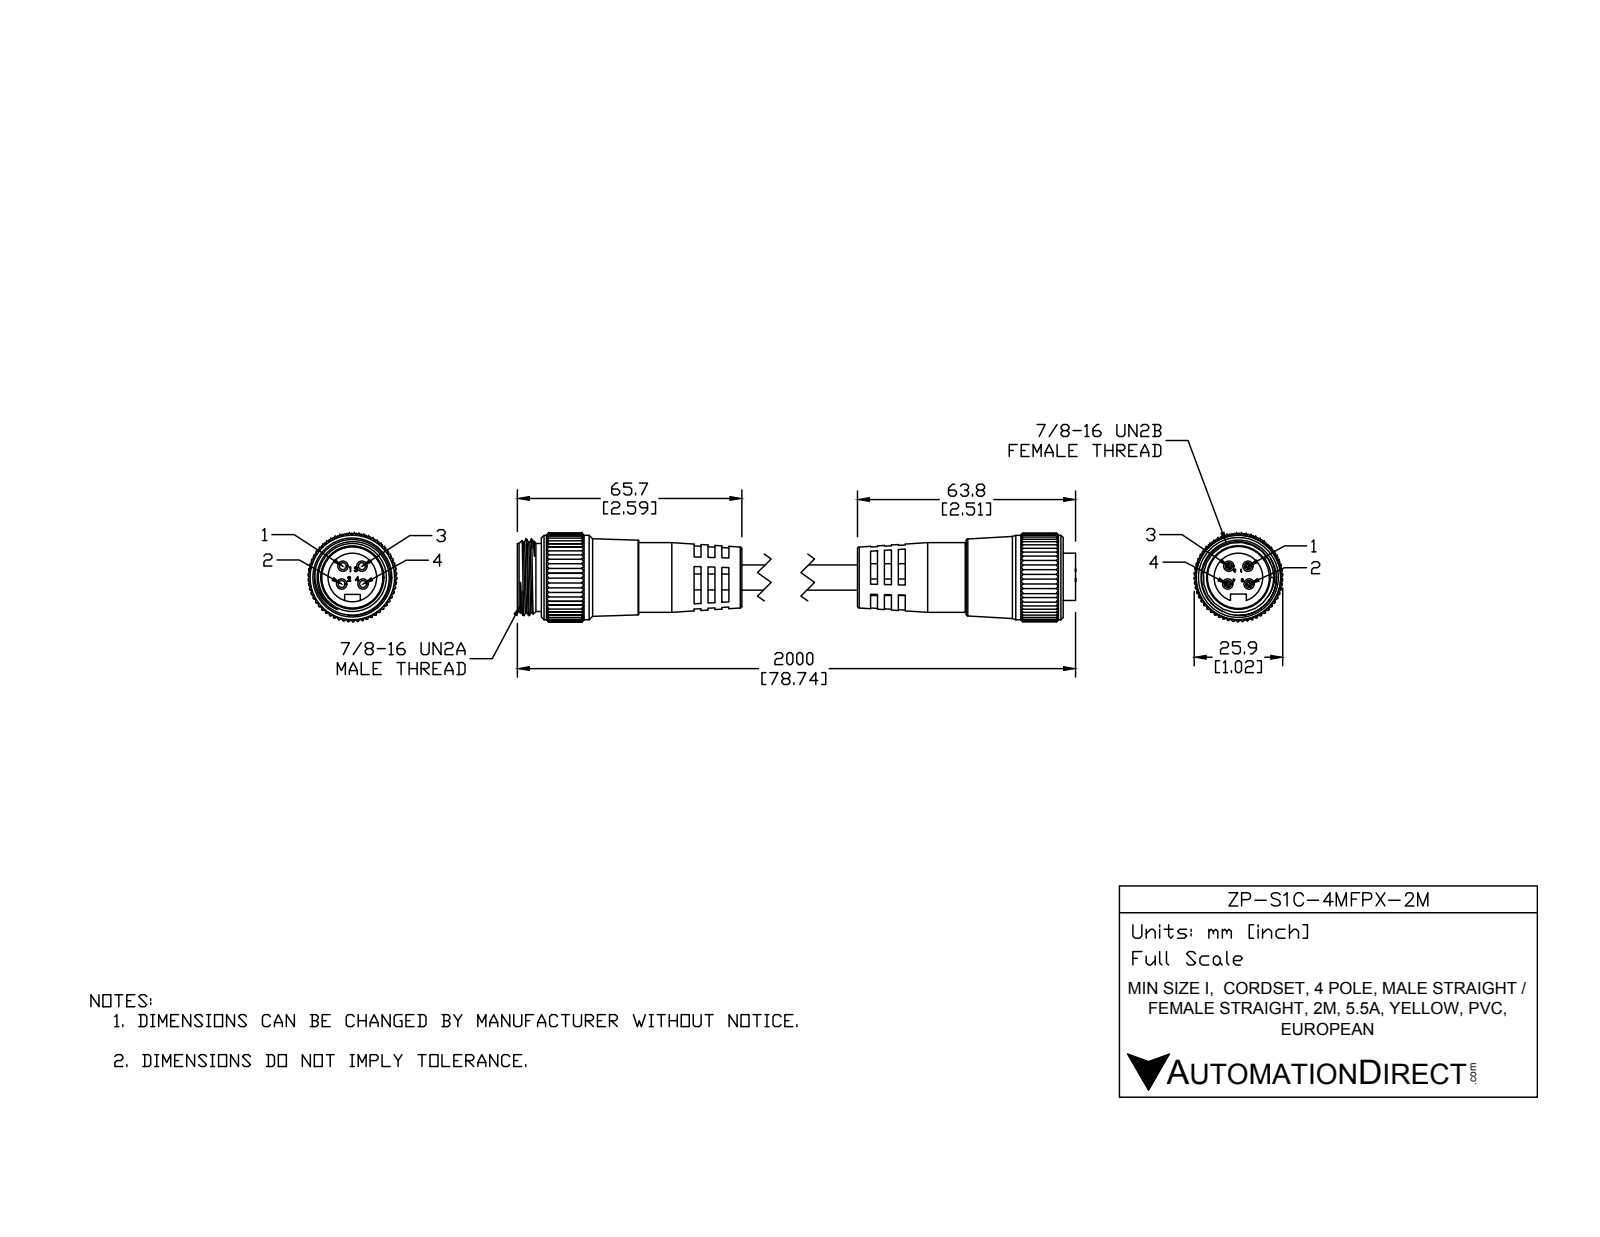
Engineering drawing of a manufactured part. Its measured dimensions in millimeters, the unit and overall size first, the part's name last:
Units: millimetres
Overall size (bounding box): 229.66 × 25.84 × 25.83
Round holes (diameter × count): ⌀3.05 ×4, ⌀19.96 ×1, ⌀20.45 ×1, ⌀21 ×1
Round bosses / shafts (diameter × count): ⌀3.05 ×4, ⌀2 ×4, ⌀24.68 ×1, ⌀22.22 ×1, ⌀20.4 ×1, ⌀19.5 ×1, ⌀17.88 ×1, ⌀14.22 ×1
Partial cylindrical surfaces — rounded edges, fillets, slot ends (radius × count): R0.25 ×165, R2.29 ×1, R5.25 ×1, R12.93 ×1
Main face-to-face distances: 2, 4.02, 117.68, 113.65, 4.03, 125.74, 59.84, 4.04, 121.7, 121.72
Hole centre spacings: 3.67, 5.24, 4.32, 4.33, 5.59, 6.24, 7.89, 7.9
Volume: 51 474 mm³ · Surface area: 24 731 mm²
Bodies: 8 solids, 1161 faces (427 planar, 634 cylindrical, 100 other)
Part name (STEP PRODUCT): ZP-S1C-4MFPX-2M
STEP written by: SolidWorks 2017 (AUTOMOTIVE_DESIGN)
